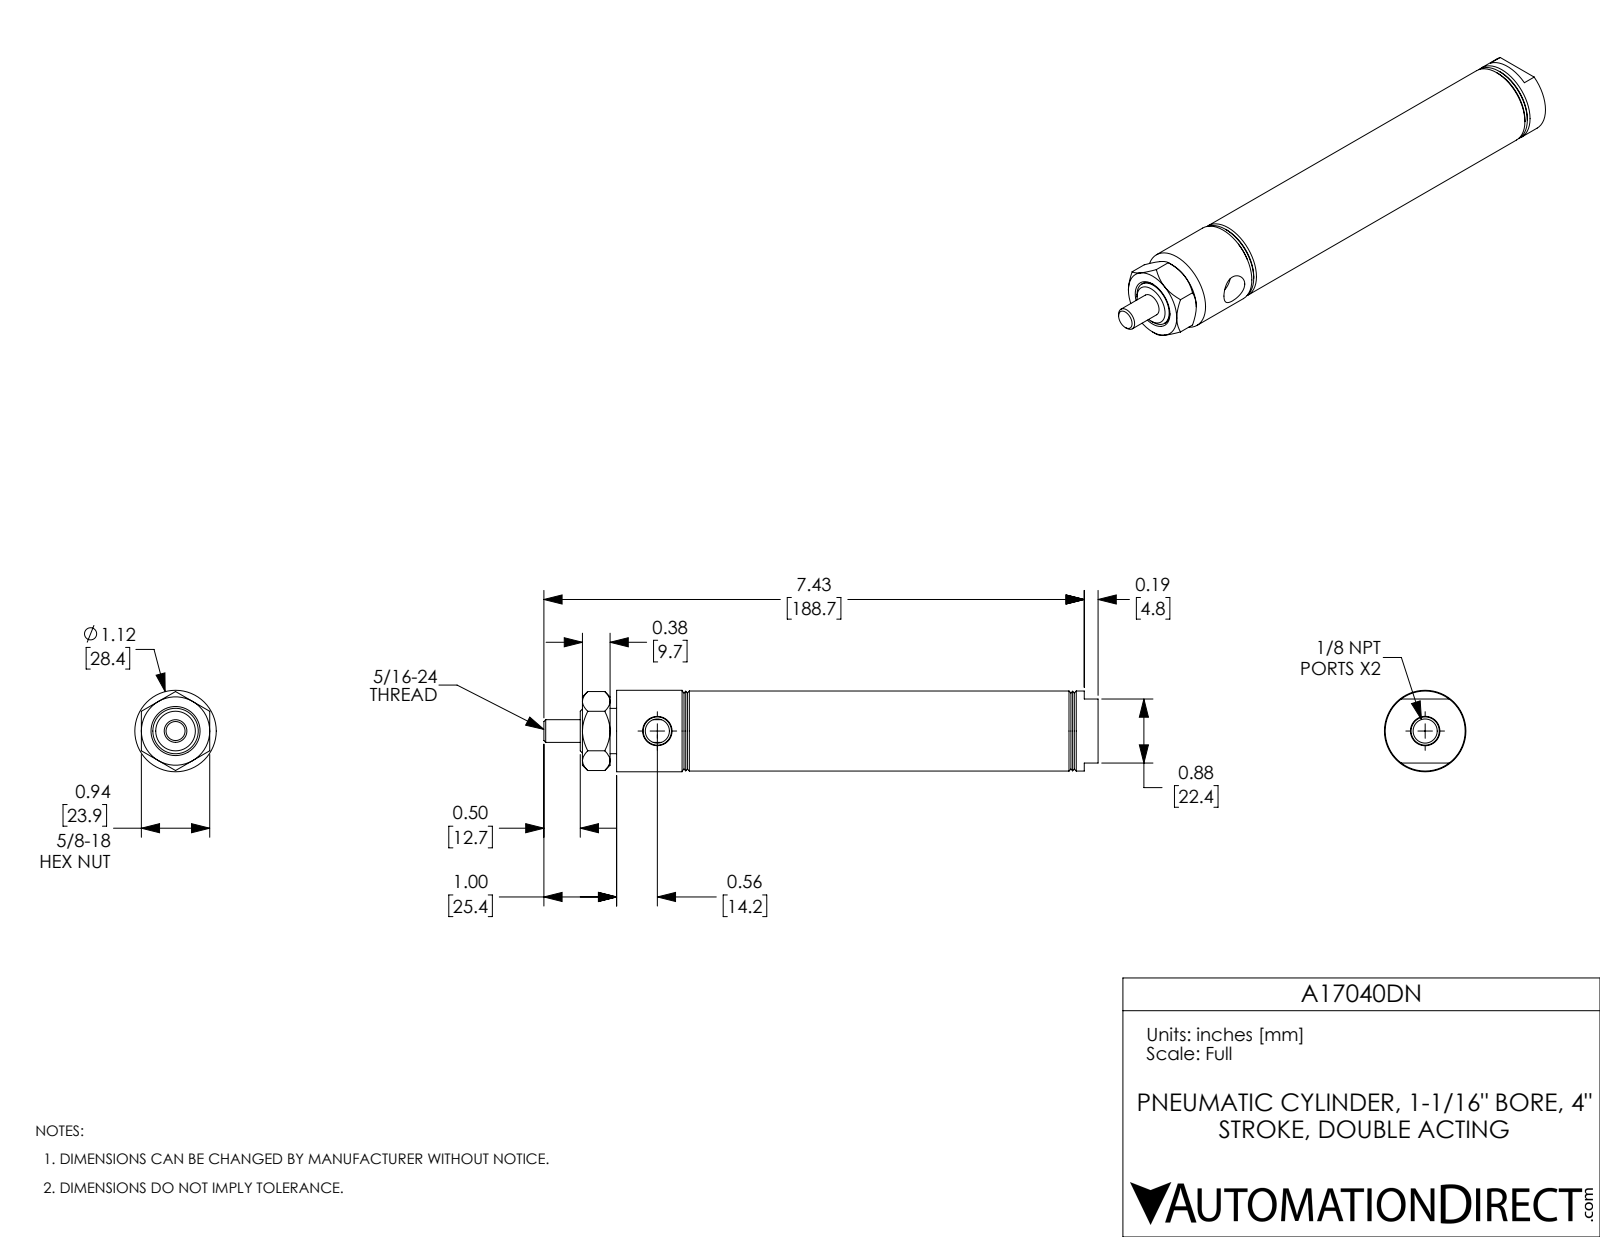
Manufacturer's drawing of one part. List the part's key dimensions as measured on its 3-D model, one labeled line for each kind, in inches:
Part name (STEP PRODUCT): A17040DN; A17040DN_Mounting Nut_D-9; A17040DN-Rod; A17040DN-MainBody
STEP written by: SolidWorks 2017 (AUTOMOTIVE_DESIGN)
Units: inches
Bodies: 3 solids, 94 faces (24 planar, 26 cylindrical, 44 other)
Overall size (bounding box): 7.62 × 1.12 × 1.12
Volume: 3.28 in³ · Surface area: 57.61 in²
Round holes (diameter × count): ⌀0.332 ×2, ⌀0.312 ×1, ⌀0.625 ×1, ⌀1.063 ×1
Round bosses / shafts (diameter × count): ⌀1.12 ×1, ⌀1.1 ×1, ⌀0.623 ×1
Main face-to-face distances: 0.5, 5.56, 4.5, 4, 1.06, 1.56, 5.56, 6.62, 5.06, 1.06
